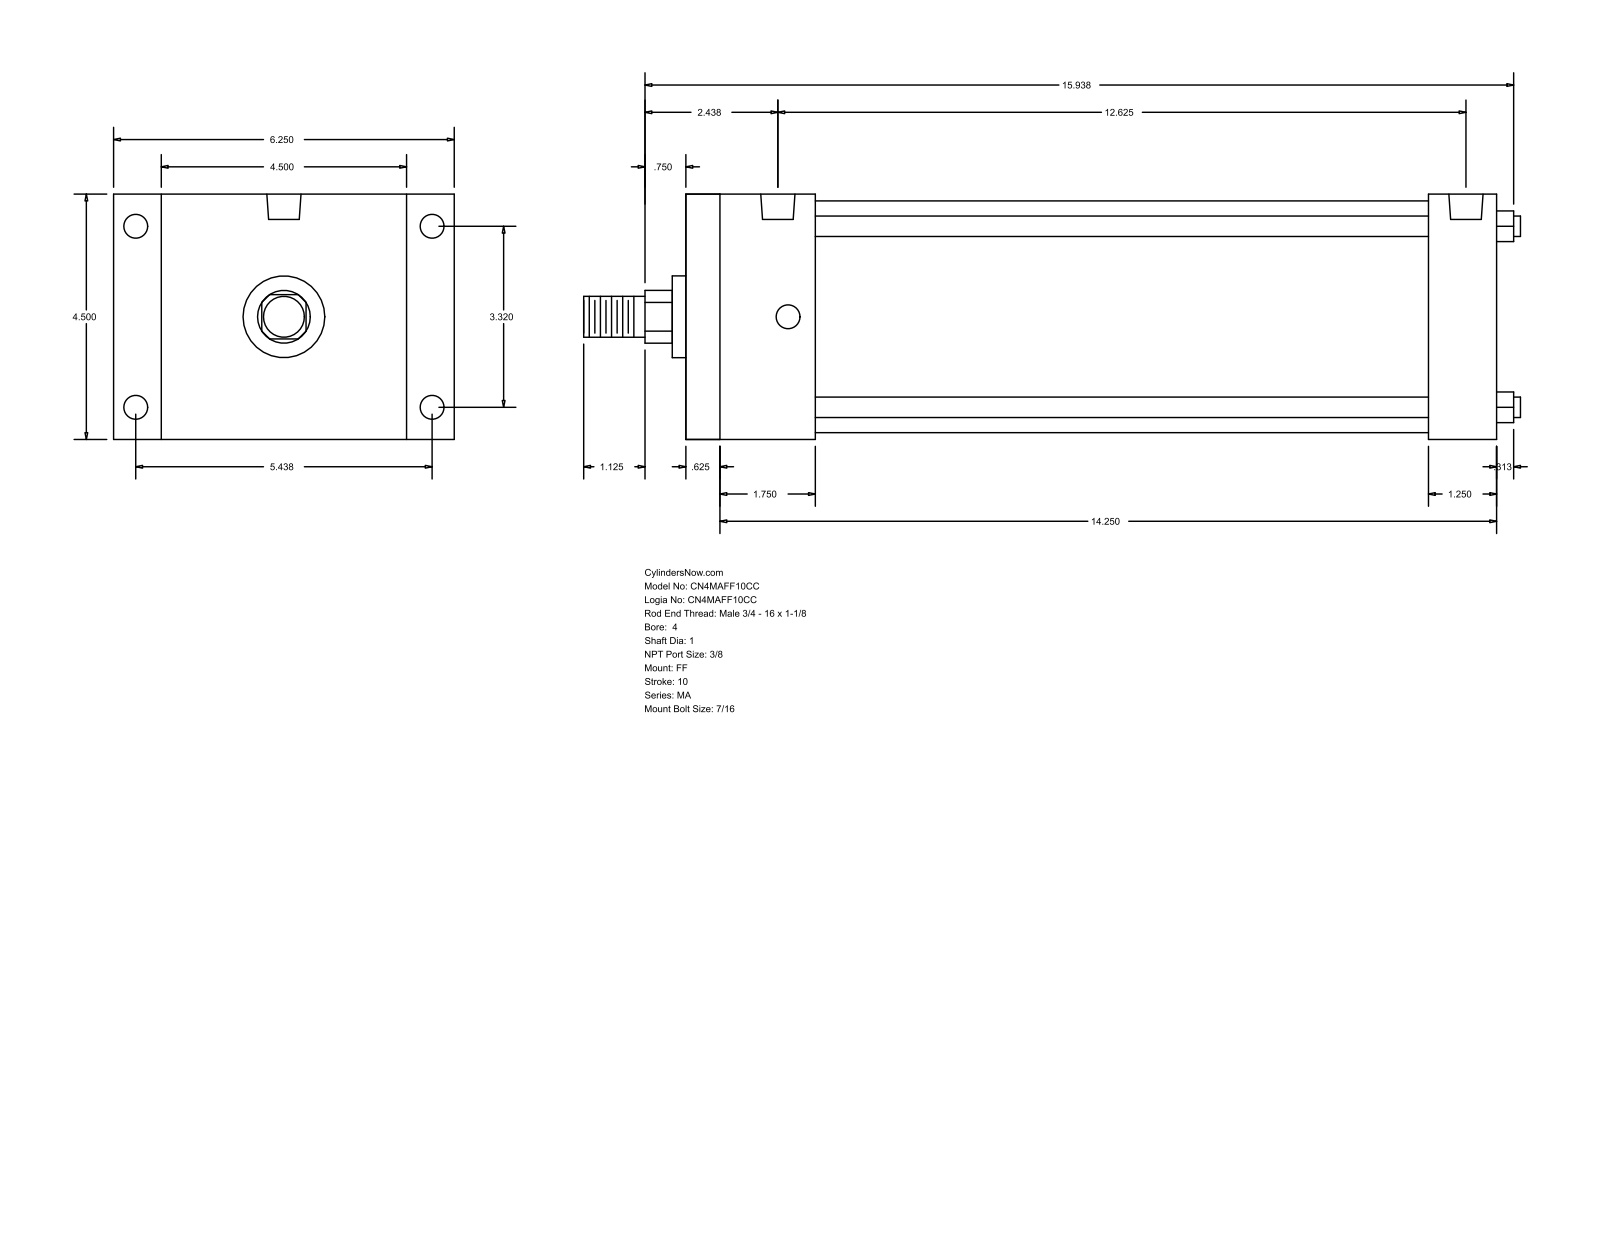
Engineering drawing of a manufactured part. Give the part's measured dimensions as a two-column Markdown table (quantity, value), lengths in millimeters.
| quantity | value |
| --- | --- |
| part name | MA_FF__0400_1 |
| STEP written by | GSSL Pune (CONFIG_CONTROL_DESIGN) |
| units | millimeters |
| bodies | 0 solids, 92 faces (64 planar, 28 cylindrical, 0 other) |
| overall size | 436.56 × 158.75 × 114.3 |
| round holes (diameter × count) | 11.11 × 8, 15.93 × 2 |
| round bosses / shafts (diameter × count) | 9.53 × 4, 107.95 × 1, 38.1 × 1, 25.4 × 1, 19.05 × 1 |
| partial cylindrical surfaces (radius × count) | 12.29 × 1 |
| main face-to-face distances | 114.3, 377.83, 15.87, 361.96, 22.23, 136.53, 346.07, 330.2, 31.76, 60.33 |
| hole center spacings | 84.32, 138.12, 161.82, 311.15, 4.76, 4.77, 315.91, 315.92 |
